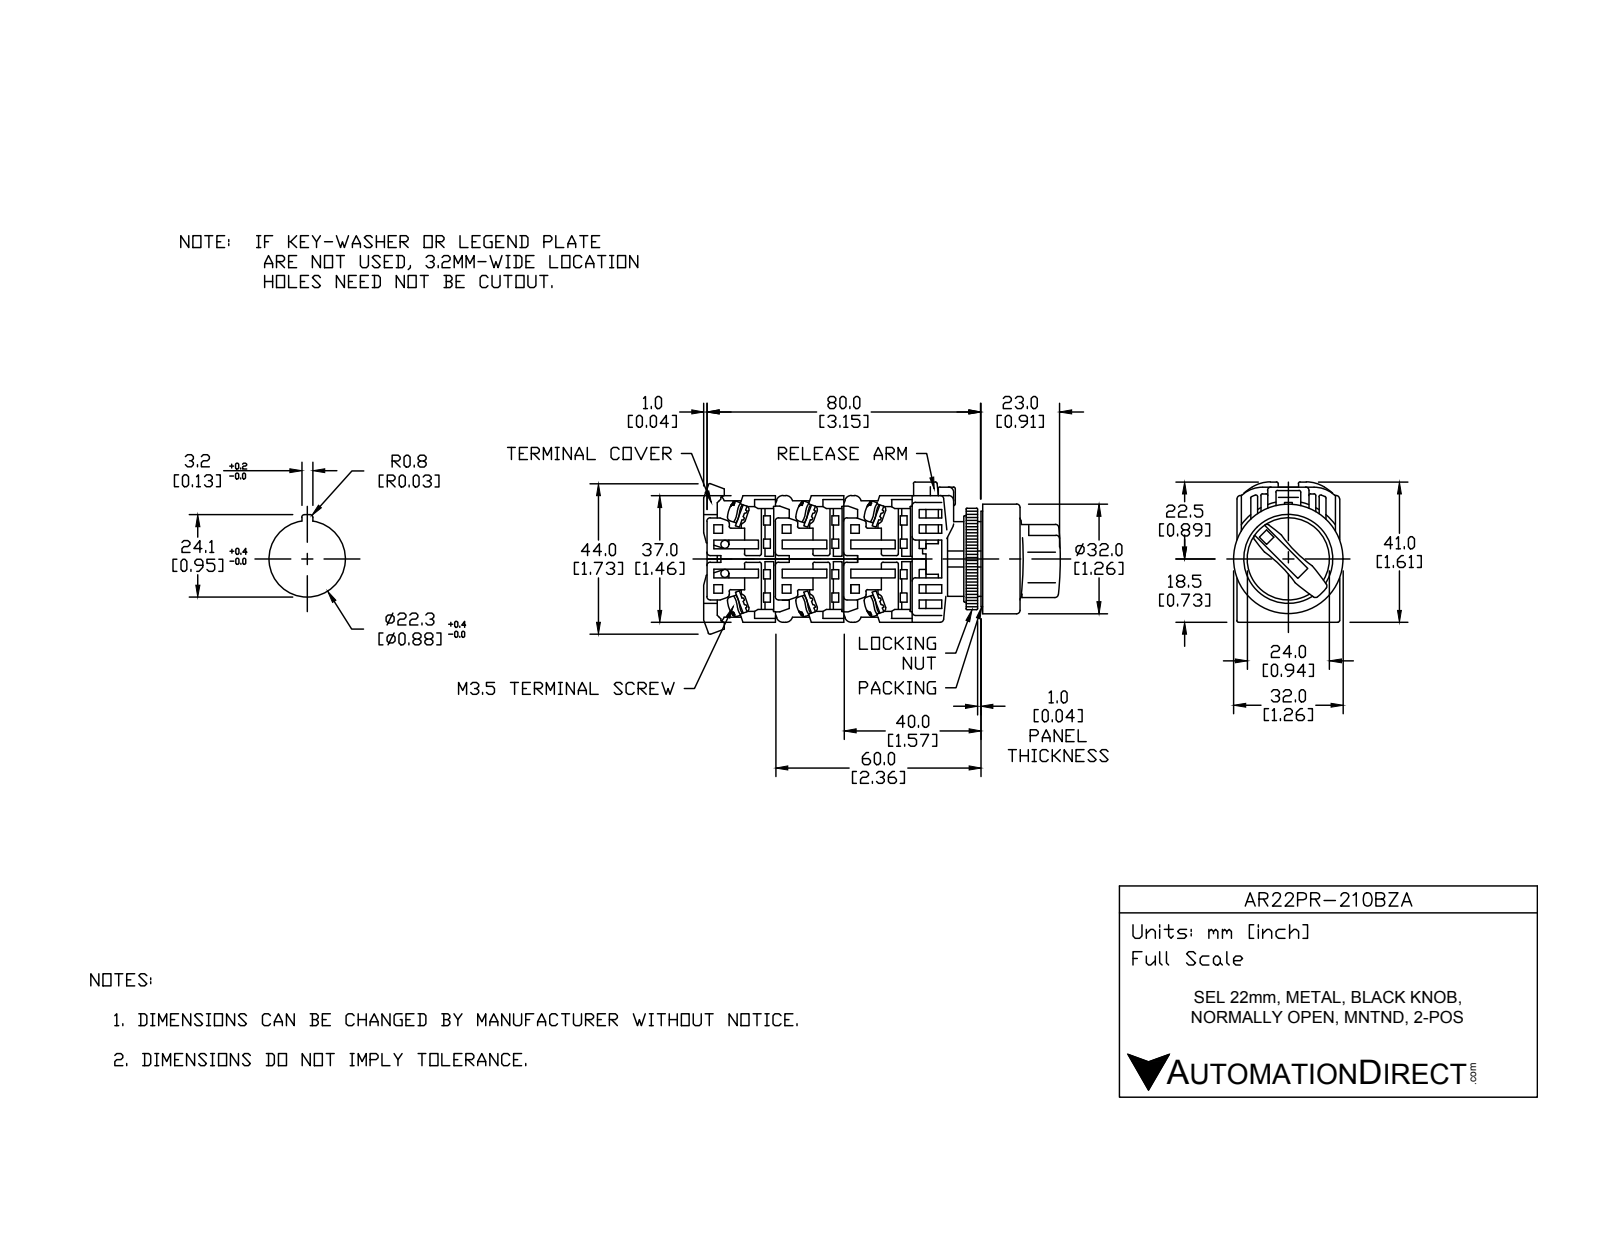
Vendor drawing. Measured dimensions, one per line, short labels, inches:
name: AR22PR-210BZA
written by: SolidWorks 2017 (AUTOMOTIVE_DESIGN)
unit: in
bodies: 12 solids, 322 faces (221 planar, 81 cylindrical, 20 other)
size: 2.52 × 1.614 × 1.26
volume: 1.794 in³; area: 31.2 in²
holes: 1× ⌀0.858, 1× ⌀0.866, 1× ⌀0.984, 1× ⌀1.22
bosses: 2× ⌀0.197, 1× ⌀1.26, 1× ⌀1.201, 1× ⌀1.173, 1× ⌀0.945, 1× ⌀0.856, 1× ⌀0.669
rounds: 23× R0.02, 6× R0.039, 4× R0.069, 4× R0.197, 2× R0.157, 1× R0.472, 1× R0.653, 1× R0.693
face distances: 0.039, 0.118, 1.122, 0.709, 0.079, 1.142, 0.433, 1.181, 0.413, 0.315
